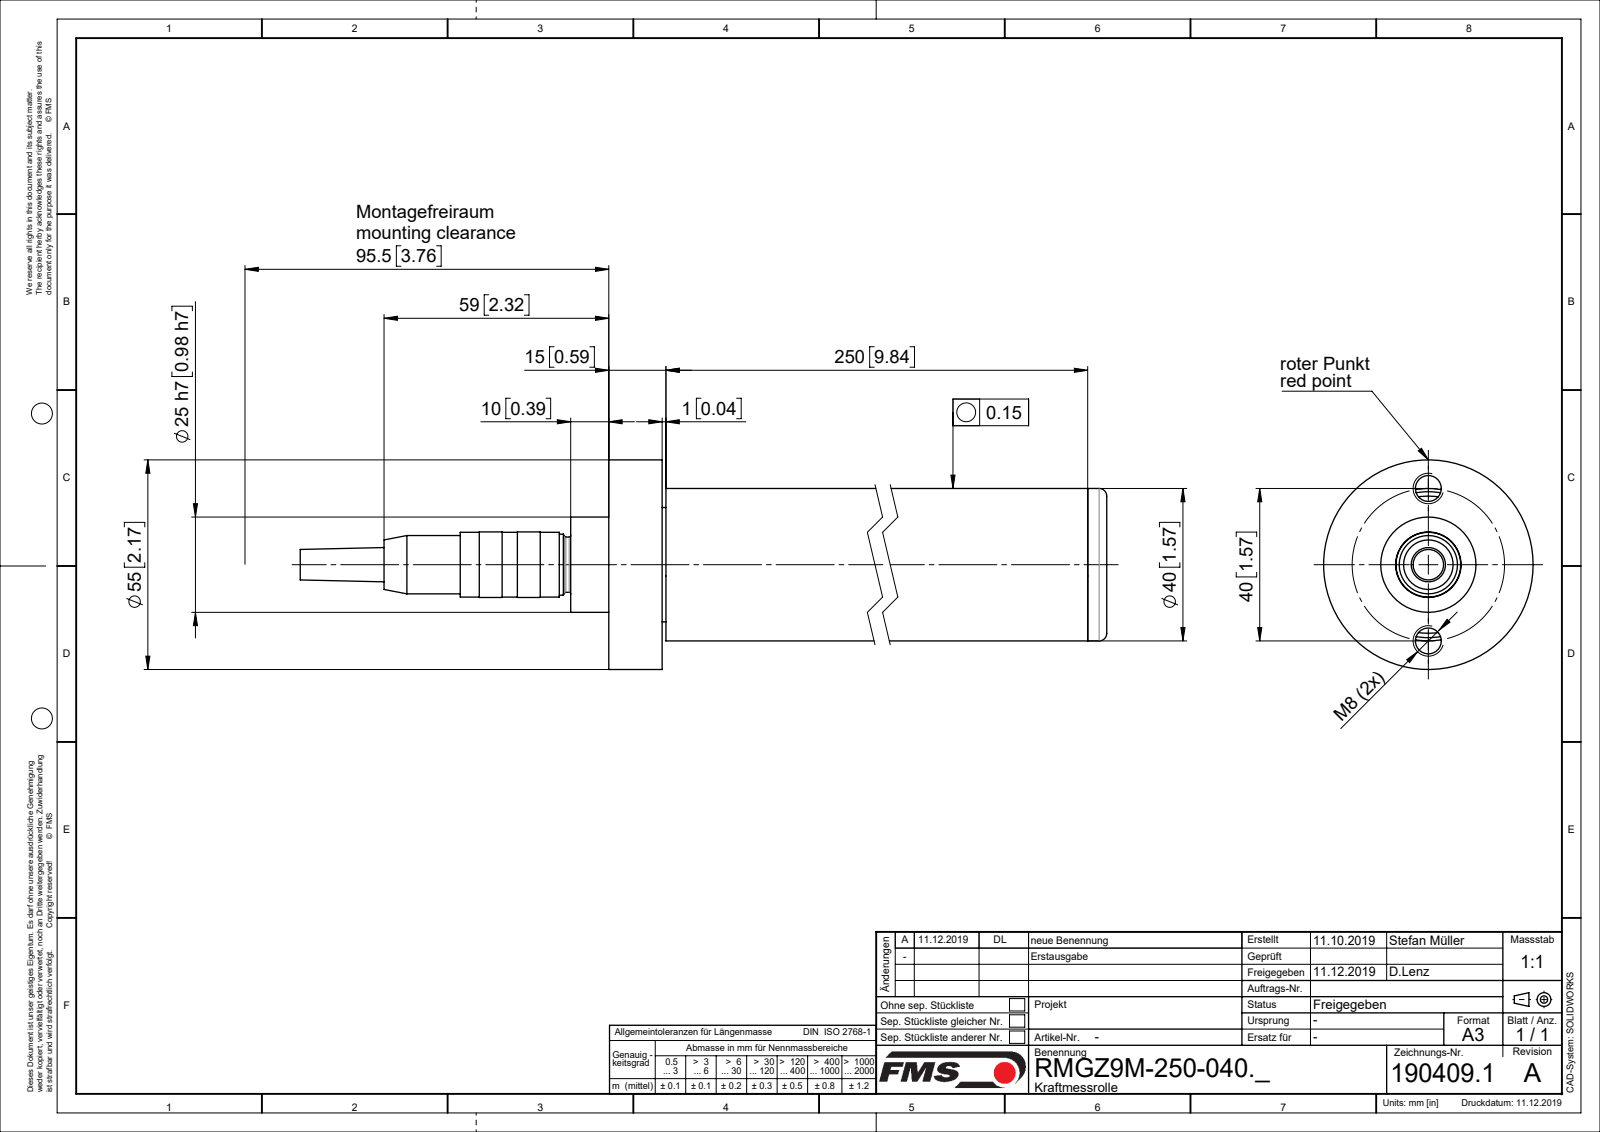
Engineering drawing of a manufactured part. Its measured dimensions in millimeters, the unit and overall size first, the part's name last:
Units: millimetres
Overall size (bounding box): 351 × 55 × 55
Round holes (diameter × count): ⌀6.91 ×2, ⌀10 ×1, ⌀11.5 ×1, ⌀12 ×1, ⌀13.3 ×1, ⌀26.3 ×1, ⌀27 ×1, ⌀28 ×1, ⌀32 ×1, ⌀36 ×1
Round bosses / shafts (diameter × count): ⌀55 ×1, ⌀40 ×1, ⌀31.3 ×1, ⌀25 ×1, ⌀17.2 ×1, ⌀17 ×1, ⌀16 ×1, ⌀15.3 ×1
Main face-to-face distances: 16, 14, 7.4, 30, 2.6, 81, 269.5, 255.5, 2.5, 251
Hole centre spacings: 20, 40
Volume: 200 535 mm³ · Surface area: 104 443 mm²
Bodies: 6 solids, 188 faces (46 planar, 88 cylindrical, 54 other)
Part name (STEP PRODUCT): R1904091_STP; R5159004; TEIL1; R51589 (+3 more)
STEP written by: Mechanical Desktop 2009 (CONFIG_CONTROL_DESIGN)
